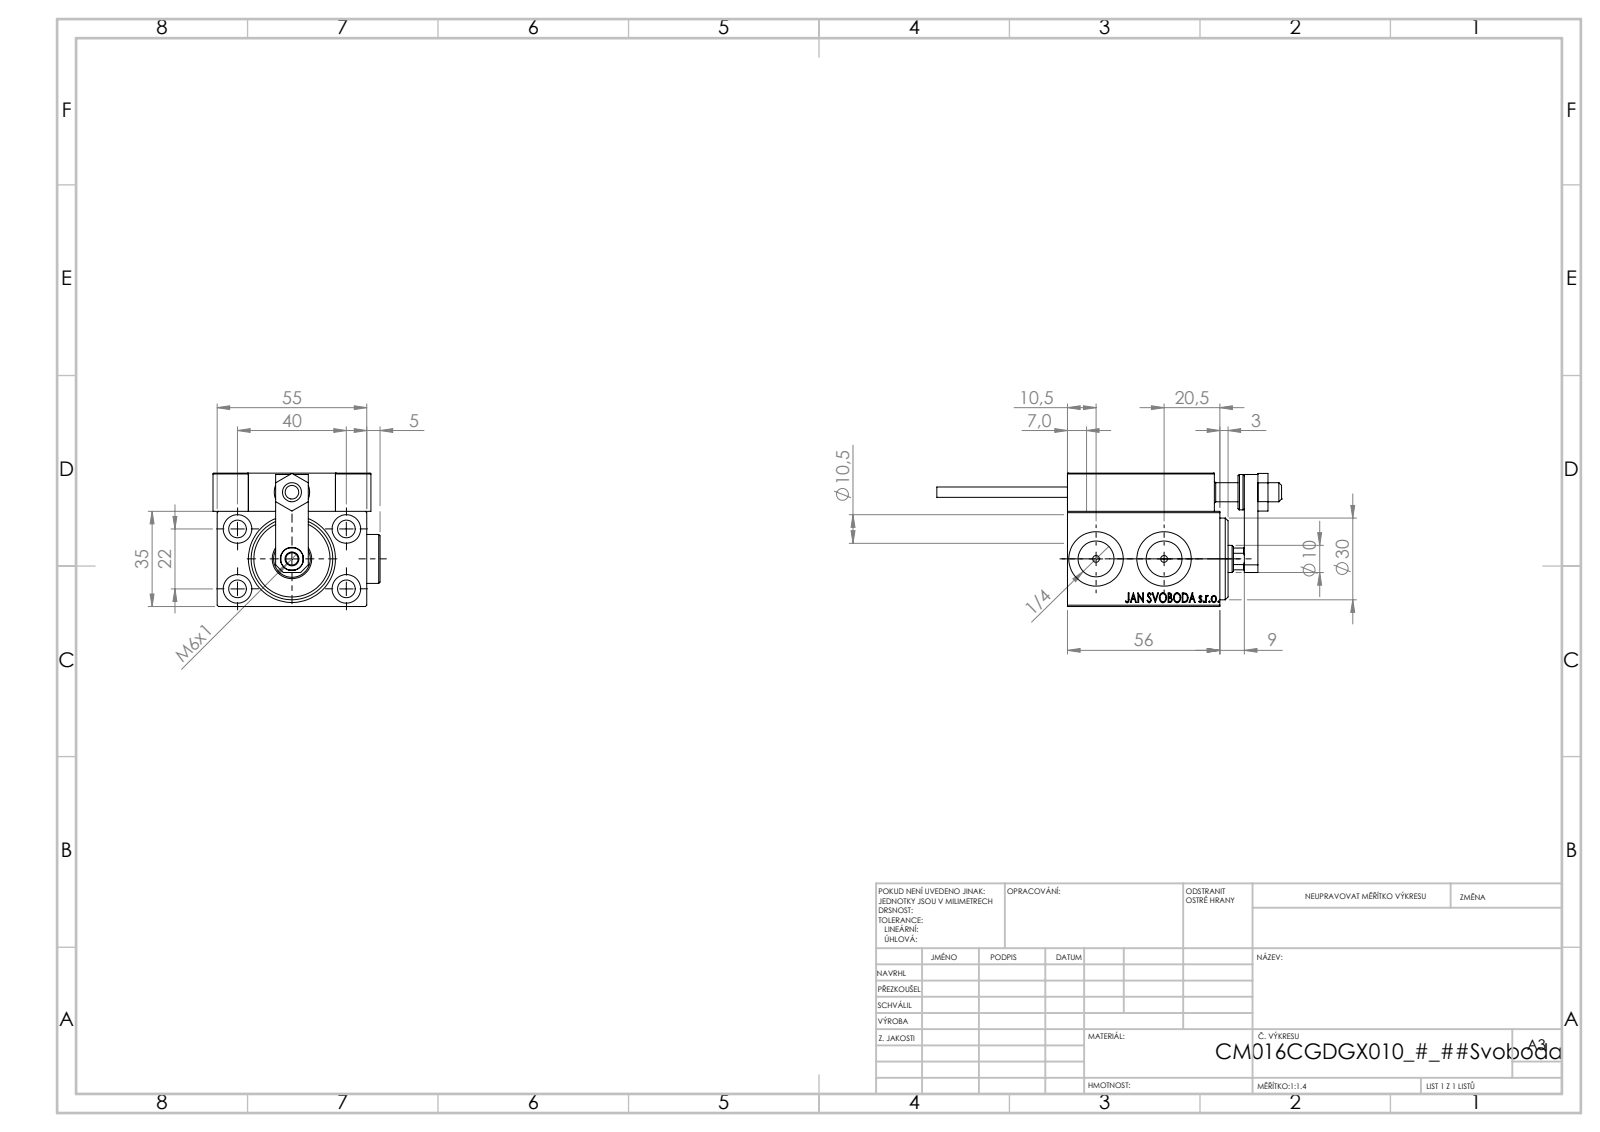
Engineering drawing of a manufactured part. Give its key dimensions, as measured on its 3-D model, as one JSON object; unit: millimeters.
{"part_name": "MAGNET; ALLEN BOLT D5; SWITCH X; SWITCH DIM B,W (+8 more)", "step_written_by": "SolidWorks 2019 (CONFIG_CONTROL_DESIGN)", "units": "millimeters", "bodies": {"solids": 25, "faces": 1339, "planar": 595, "cylindrical": 206, "other": 538}, "overall_size": [126.7, 61.4, 49], "volume_mm3": 134628, "surface_area_mm2": 52697, "round_holes": [[8, 5], [3.2, 4], [4, 4], [6.5, 4], [10.5, 4], [2.5, 2], [5, 2], [13.16, 2], [20, 2], [4.5, 1], [7, 1], [8.5, 1]], "round_bosses_or_shafts": [[18, 2], [5, 2], [3.8, 2], [13, 1], [11, 1]], "partial_cylinders_radius": [[0.3, 26], [3, 2], [4.5, 1]], "face_to_face_distances": [49, 35, 5, 14, 3, 7, 10, 1.5, 44, 55], "hole_center_spacings": [22.83, 8.25, 11.37, 20, 22, 23.41, 24.13, 29.59]}
